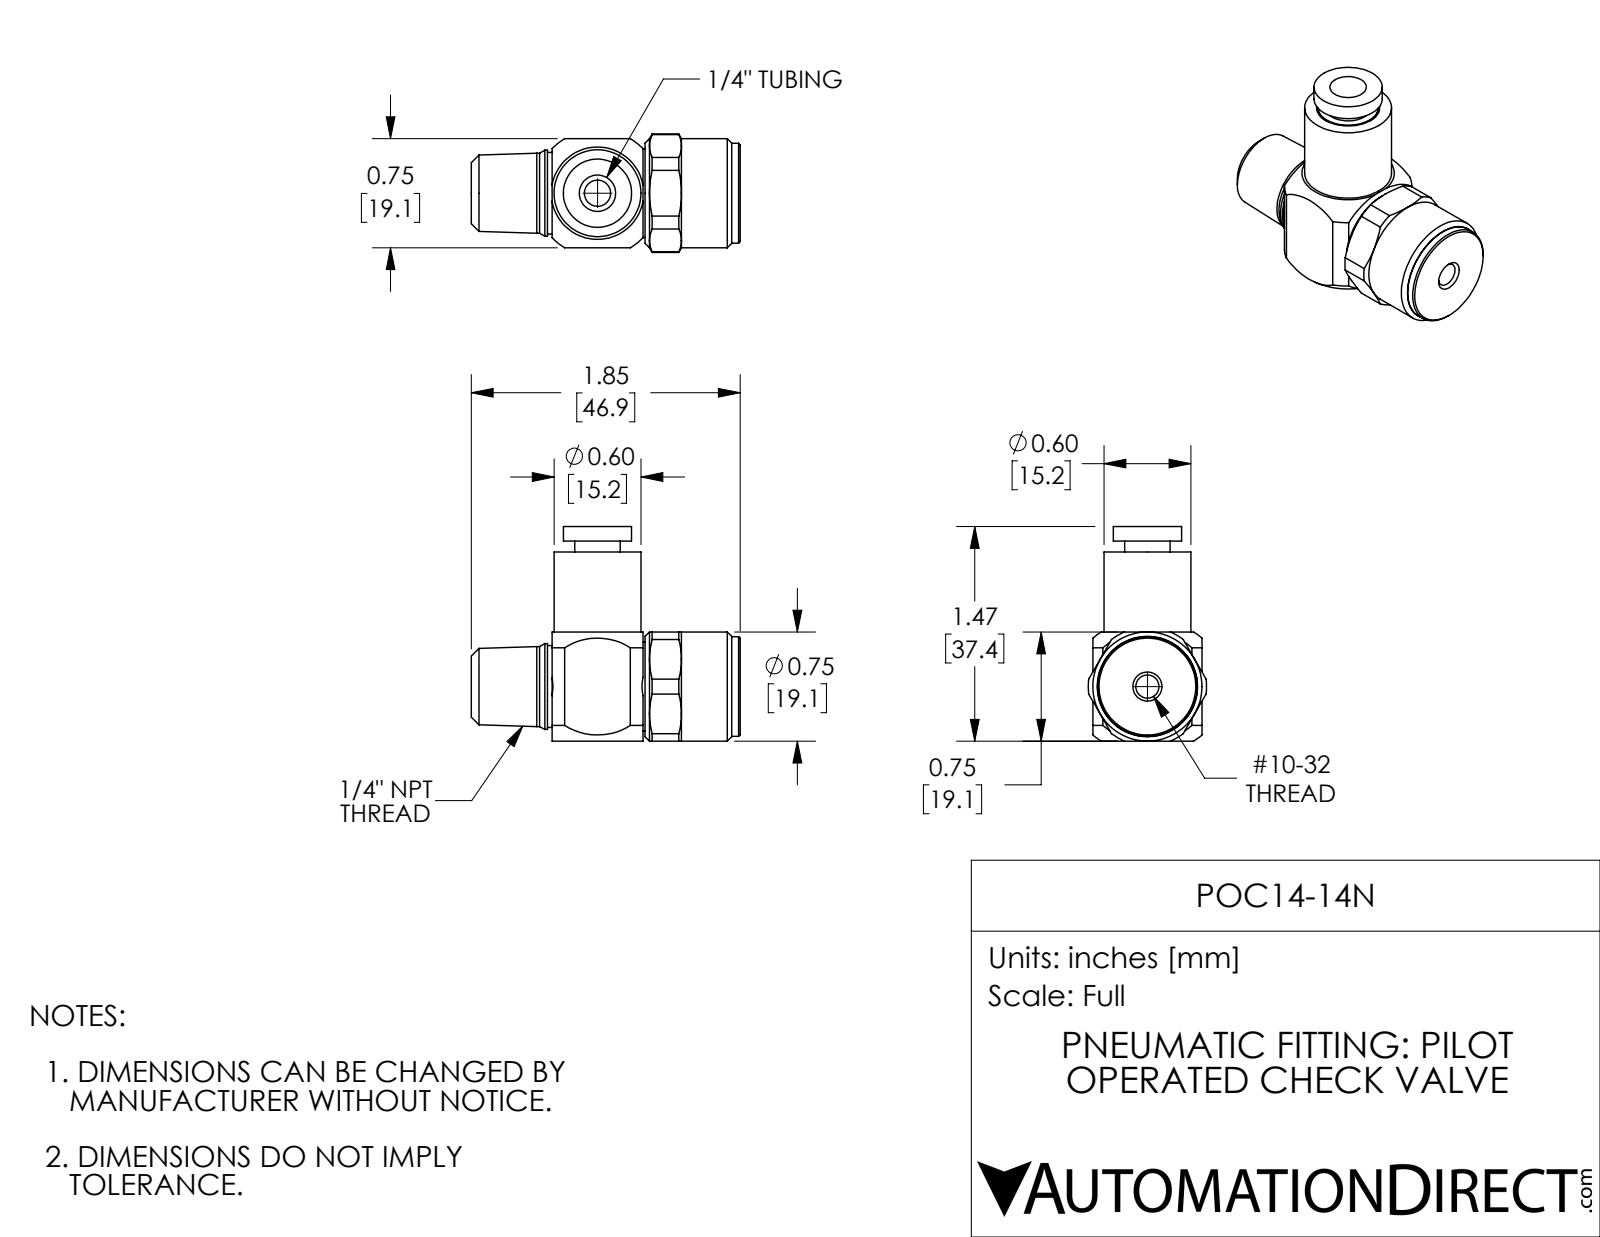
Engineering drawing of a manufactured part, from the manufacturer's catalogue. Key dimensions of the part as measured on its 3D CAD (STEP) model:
Part name (STEP PRODUCT): POC14-14N
STEP written by: SolidWorks 2018 (AUTOMOTIVE_DESIGN)
Units: inches
Bodies: 3 solids, 140 faces (35 planar, 57 cylindrical, 48 other)
Overall size (bounding box): 1.848 × 1.474 × 0.813
Volume: 0.805 in³ · Surface area: 12.49 in²
Round holes (diameter × count): ⌀0.159 ×1, ⌀0.18 ×1, ⌀0.25 ×1, ⌀0.258 ×1, ⌀0.35 ×1, ⌀0.381 ×1, ⌀0.62 ×1, ⌀0.625 ×1
Round bosses / shafts (diameter × count): ⌀0.75 ×1, ⌀0.685 ×1, ⌀0.608 ×1, ⌀0.597 ×1, ⌀0.591 ×1, ⌀0.575 ×1, ⌀0.562 ×1, ⌀0.55 ×1
Partial cylindrical surfaces — rounded edges, fillets, slot ends (radius × count): R0.406 ×1, R0.437 ×1
Main face-to-face distances: 0.32, 0.75, 1.3, 0.262, 0.058, 0.1, 0.973, 1.235, 1.293, 0.031
